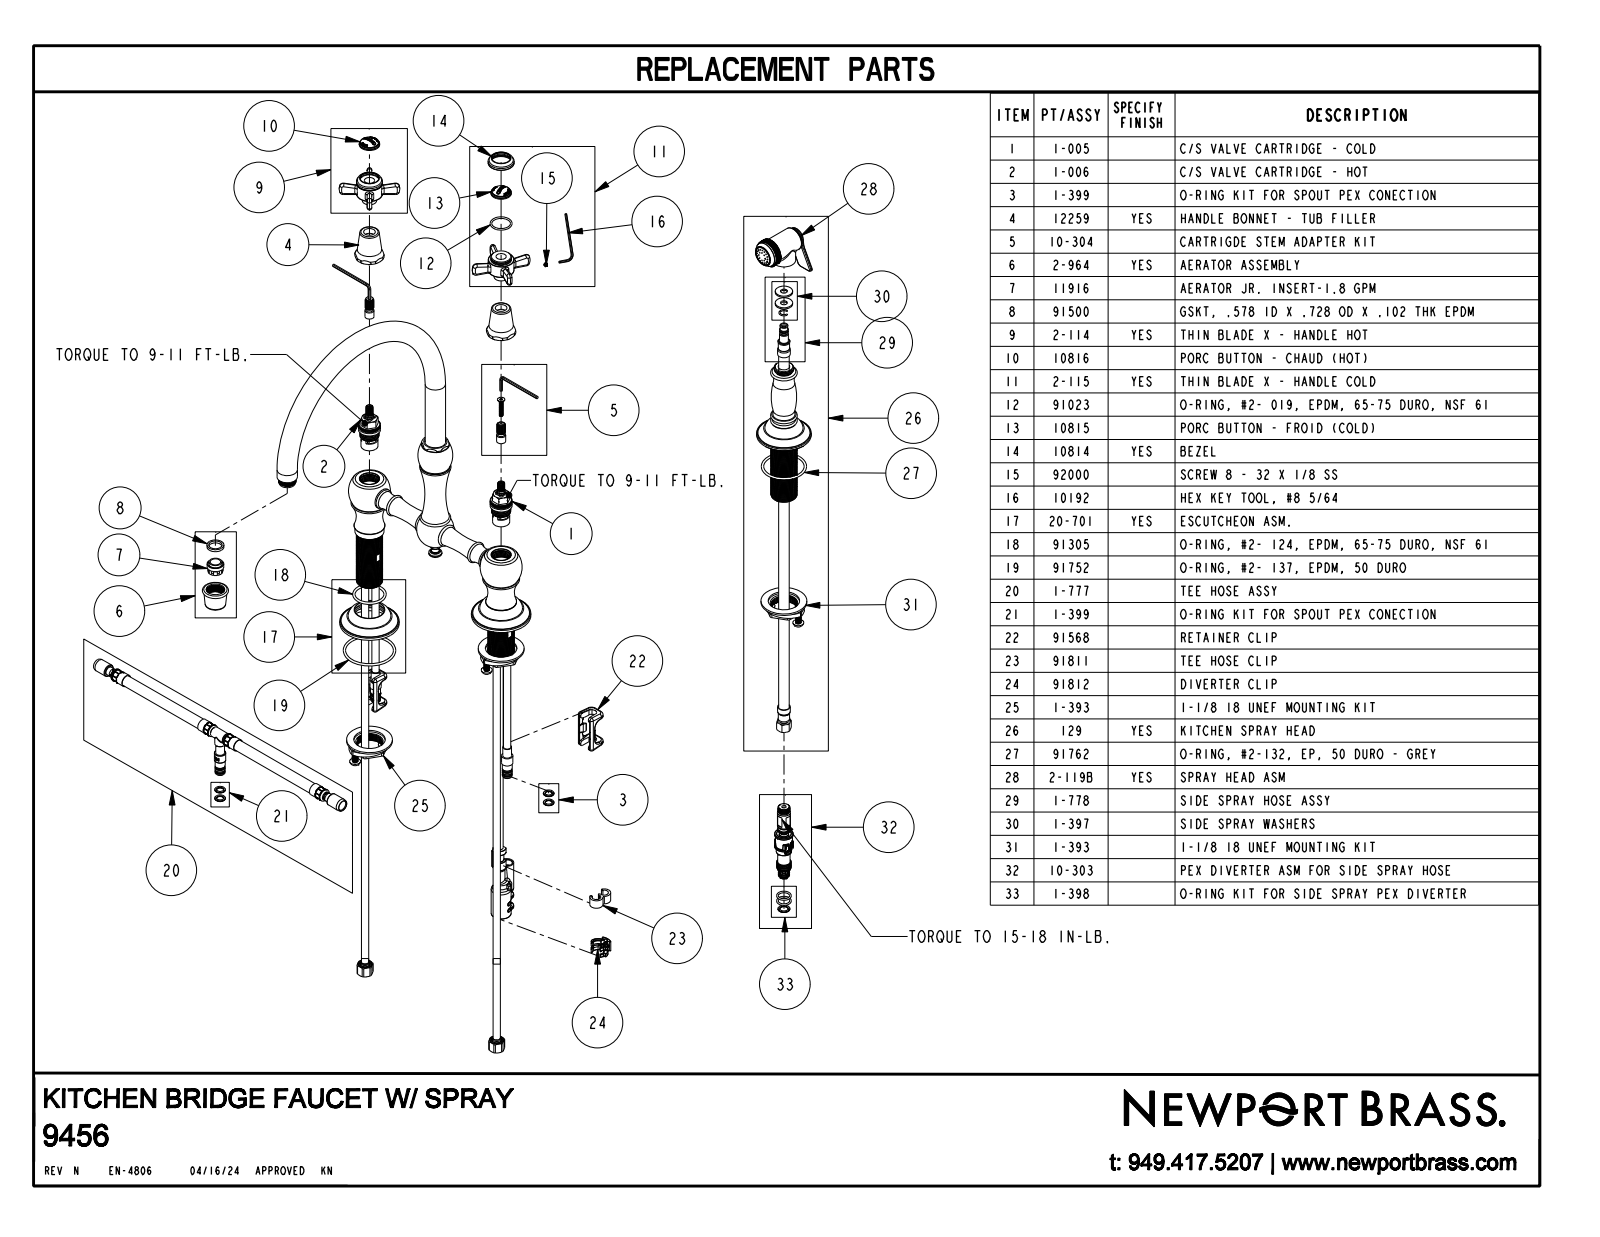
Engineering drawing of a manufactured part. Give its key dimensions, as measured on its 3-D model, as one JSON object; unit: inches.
{"part_name": "9456", "step_written_by": "CREO PARAMETRIC BY PTC INC, 2018400 (AUTOMOTIVE_DESIGN)", "units": "inches", "bodies": {"solids": 4, "faces": 1648, "planar": 725, "cylindrical": 491, "other": 432}, "overall_size": [15.136, 15.1, 10.95], "volume_in3": 40.68, "surface_area_in2": 197.2, "round_holes": [[0.06, 1], [0.231, 1], [0.9, 1], [0.968, 1]], "round_bosses_or_shafts": [[2.35, 3], [1.115, 2], [1.1, 2], [0.89, 2], [0.875, 2], [0.603, 2], [1.11, 1], [1.023, 1]], "partial_cylinders_radius": [[0.011, 28], [0.1, 25], [0.025, 17], [0.04, 15], [0.006, 14], [0.005, 10], [0.015, 10], [0.006, 8]], "face_to_face_distances": [0.2, 5.656, 4.89, 0.13, 4.52, 0.37, 5.856, 5.456, 5.47, 0.95]}
